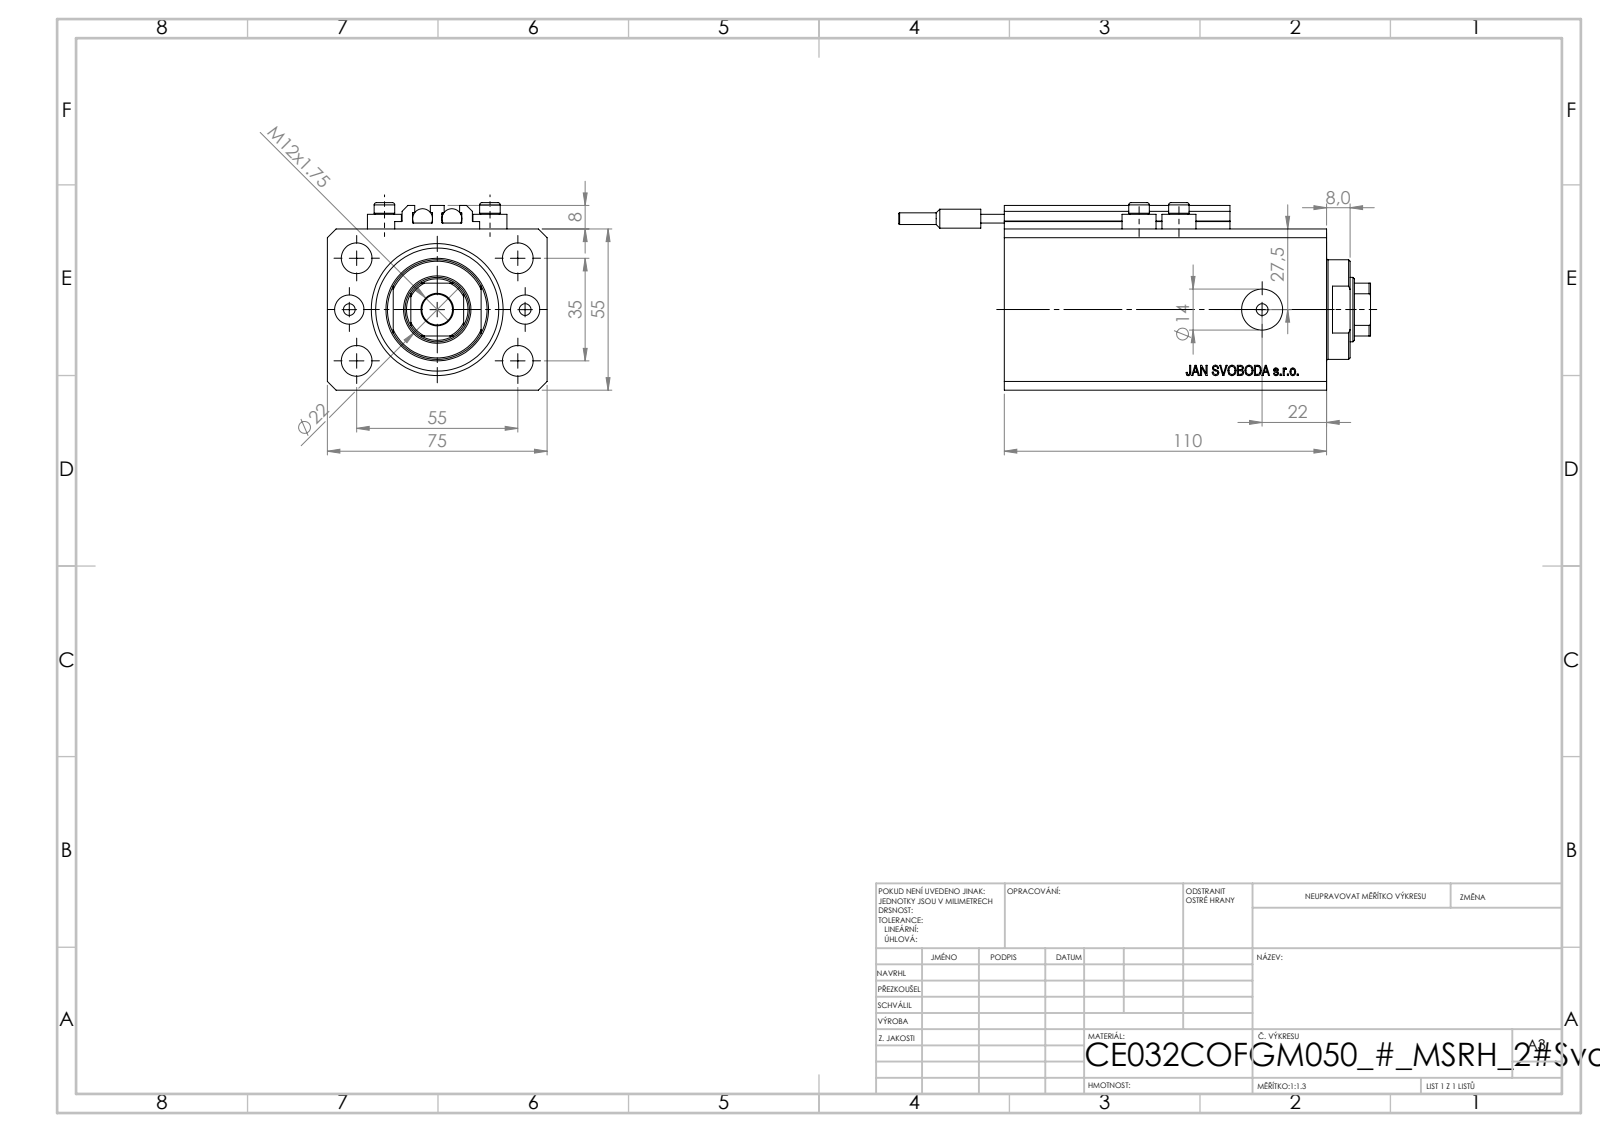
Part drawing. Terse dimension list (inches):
name: V250CE_C_VCP; SWITCH_V250CE; ALLEN BOLT V250CE; V250CE_VC_C (+1 more)
written by: SolidWorks 2019 (CONFIG_CONTROL_DESIGN)
unit: in
bodies: 10 solids, 1086 faces (536 planar, 98 cylindrical, 452 other)
size: 6.339 × 2.953 × 2.52
volume: 25.17 in³; area: 145.5 in²
holes: 8× ⌀0.157, 5× ⌀0.413, 2× ⌀0.394, 2× ⌀0.551, 1× ⌀0.866, 1× ⌀1.26, 1× ⌀1.772
bosses: 4× ⌀0.457, 4× ⌀0.276, 2× ⌀0.268, 2× ⌀0.256, 2× ⌀0.157, 1× ⌀1.339
rounds: 10× R0.008, 1× R0.413
face distances: 2.165, 2.953, 4.331, 0.591, 3.74, 0.118, 0.39, 3.35, 3.941, 0.079
hole spacings: 0.696, 1.283, 2.366, 0.535, 1.181, 1.378, 1.417, 1.515
